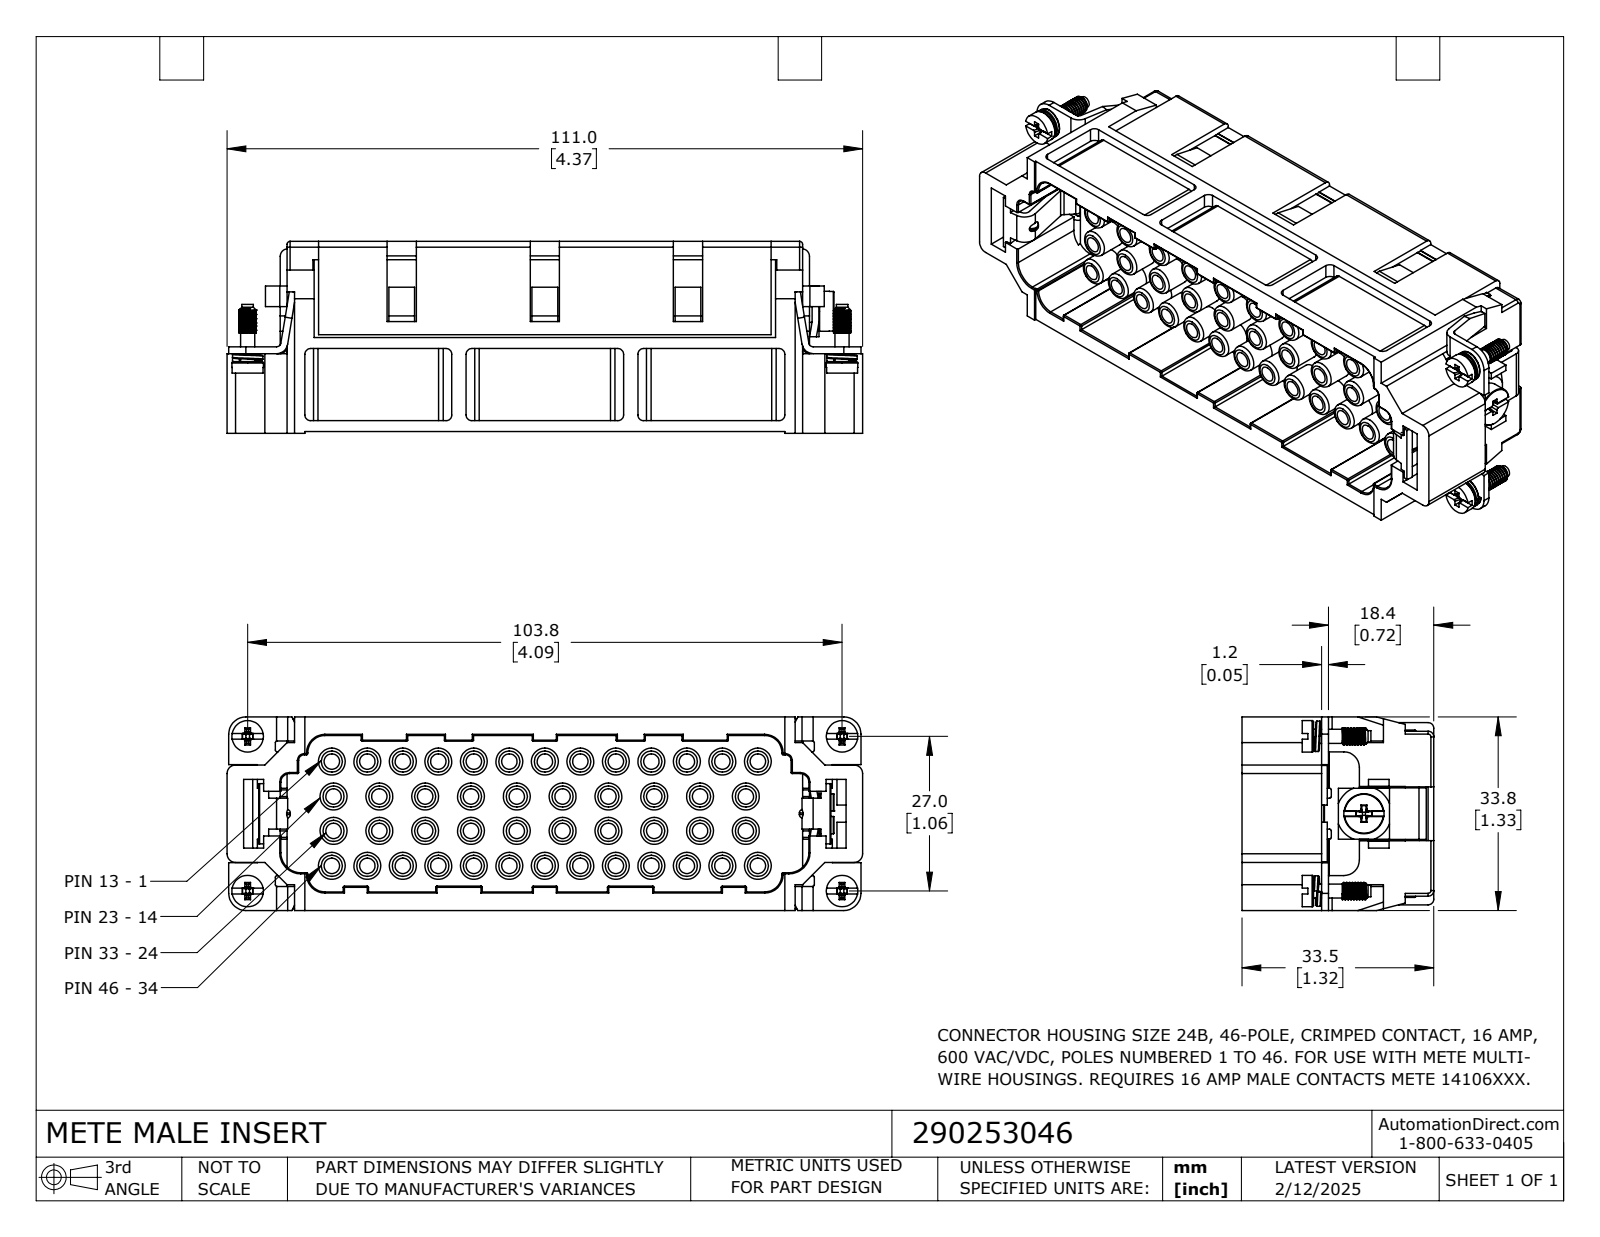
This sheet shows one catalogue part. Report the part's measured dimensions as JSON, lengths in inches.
{"part_name": "290253046", "step_written_by": "SolidWorks 2024 (CONFIG_CONTROL_DESIGN)", "units": "inches", "bodies": {"solids": 11, "faces": 2909, "planar": 1409, "cylindrical": 1046, "other": 454}, "overall_size": [4.37, 1.331, 1.319], "volume_in3": 2.97, "surface_area_in2": 86.06, "round_holes": [[0.106, 49], [0.189, 46], [0.071, 18], [0.114, 4], [0.13, 1]], "round_bosses_or_shafts": [[0.185, 46], [0.063, 18], [0.217, 4], [0.209, 4], [0.118, 4], [0.096, 4], [0.079, 4], [0.091, 3]], "partial_cylinders_radius": [[0.008, 57], [0.118, 54], [0.059, 52], [0.096, 46], [0.165, 46], [0.01, 32], [0.039, 20], [0.031, 14]], "face_to_face_distances": [0.051, 0.128, 0.028, 0.055, 1.163, 1.197, 0.039, 0.031, 0.063, 1.201], "hole_center_spacings": [0.315, 0.394, 0.63, 0.673, 0.945, 0.974, 1.26, 1.282]}
